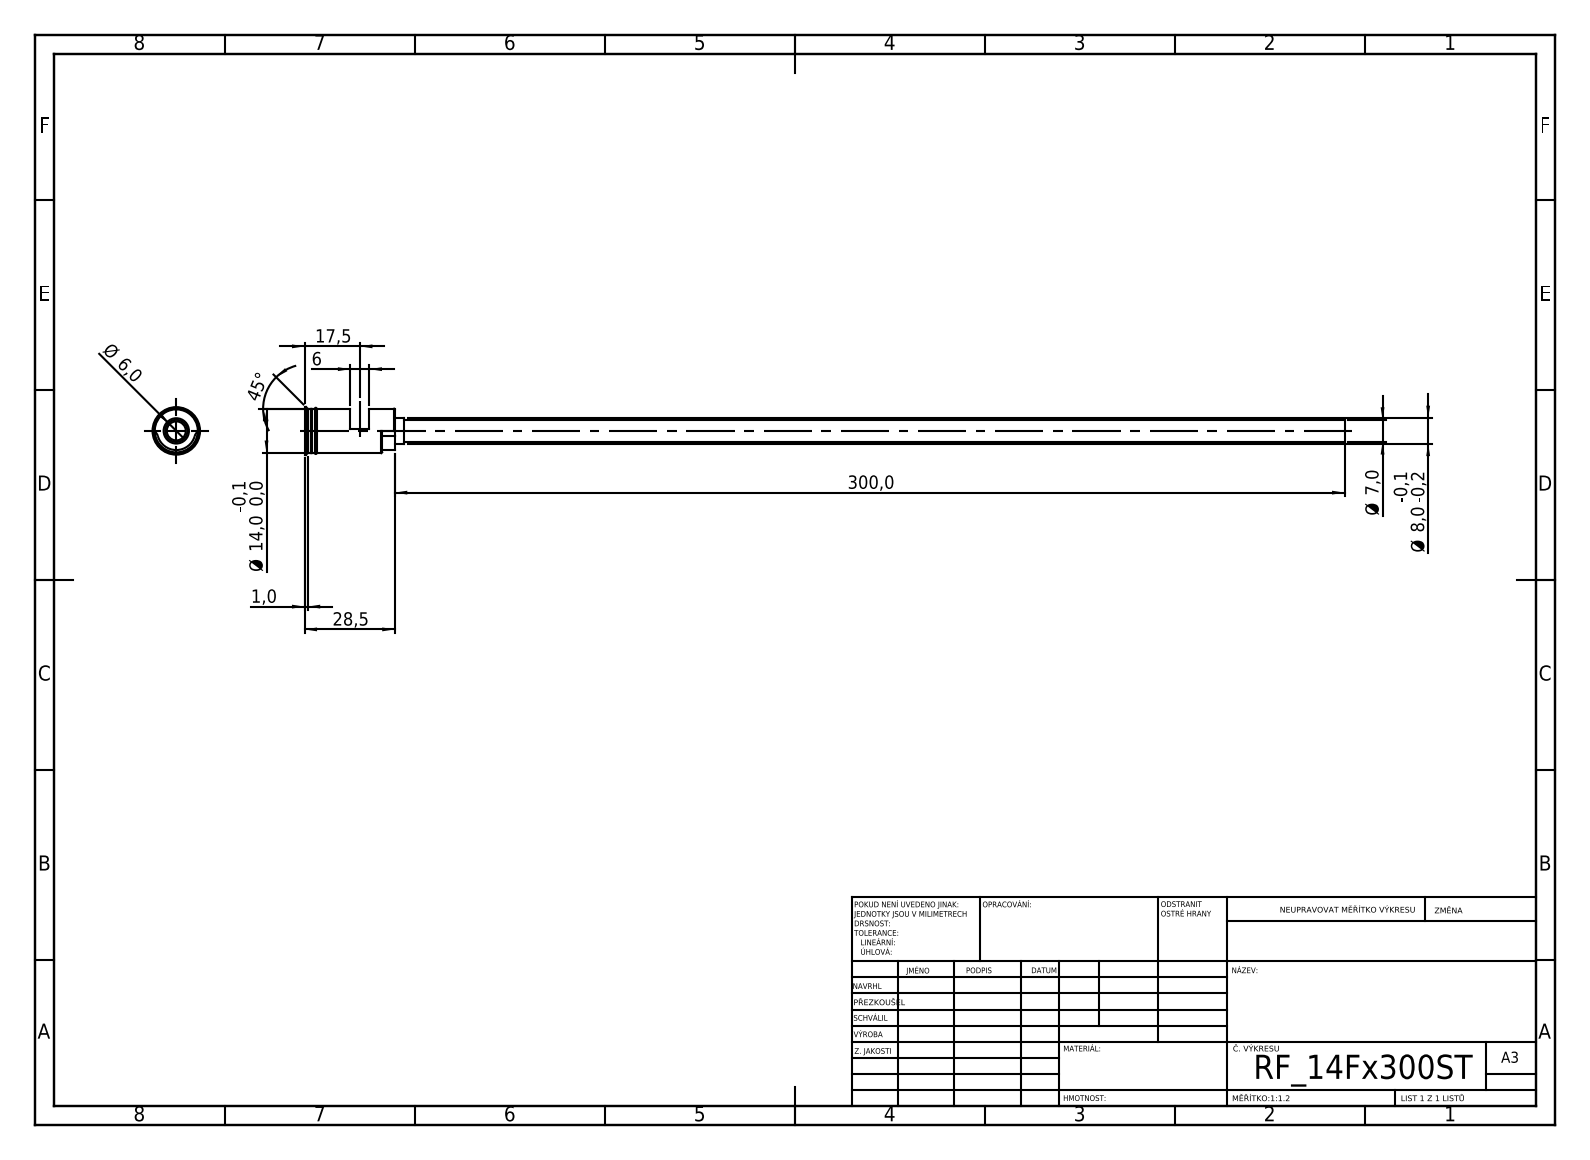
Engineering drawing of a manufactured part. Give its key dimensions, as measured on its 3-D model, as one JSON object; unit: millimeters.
{"step_written_by": "SolidWorks 2019 (CONFIG_CONTROL_DESIGN)", "units": "millimeters", "bodies": {"solids": 1, "faces": 55, "planar": 24, "cylindrical": 19, "other": 12}, "overall_size": [328.5, 15, 15], "volume_mm3": 6515, "surface_area_mm2": 14188, "round_holes": [[6, 1]], "round_bosses_or_shafts": [[15, 1], [14, 1], [13.8, 1], [8, 1], [7, 1]], "partial_cylinders_radius": [[3, 2], [6.05, 1]], "face_to_face_distances": [2, 12.5, 14.5, 14, 26.5, 28.5, 8, 6, 18.5, 20.5]}
